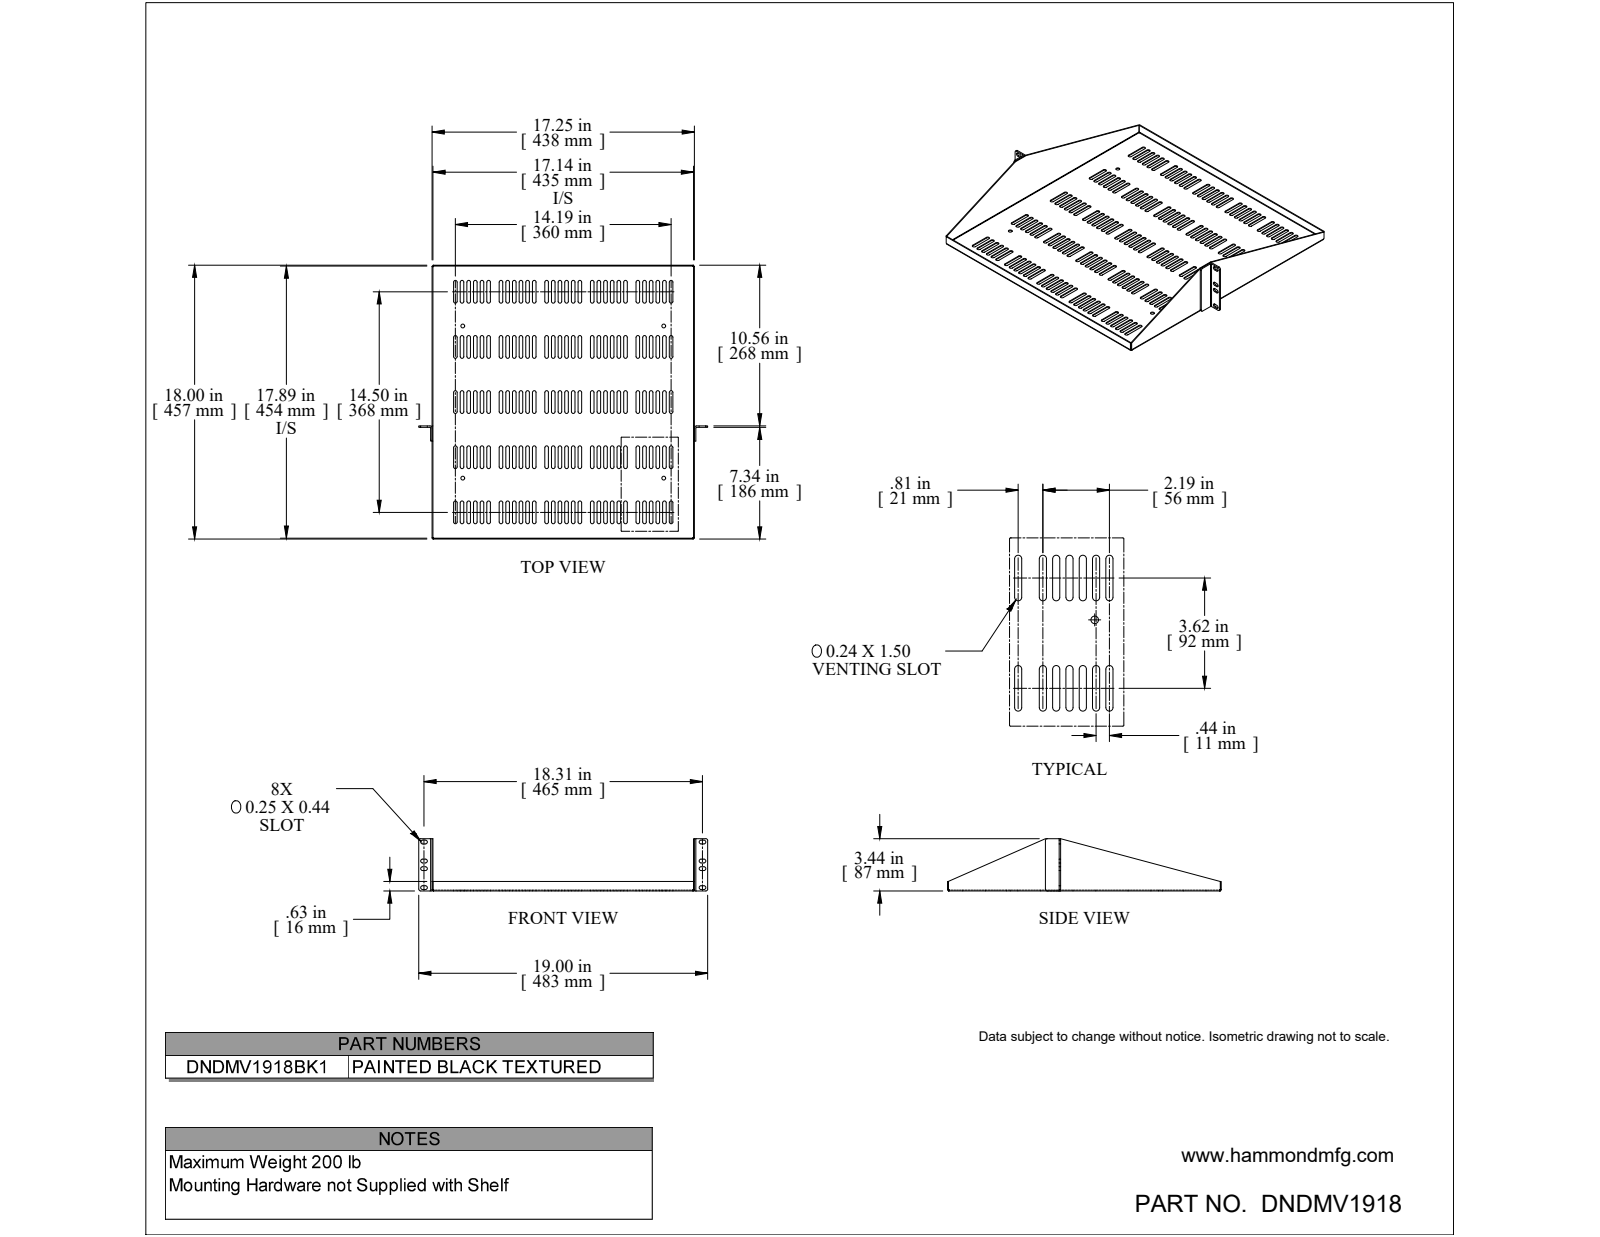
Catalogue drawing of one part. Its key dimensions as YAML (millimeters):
part_name: "DNDMV1918BK1"
step_written_by: "SolidWorks 2019 (CONFIG_CONTROL_DESIGN)"
units: millimeters
bodies: {solids: 3, faces: 714, planar: 358, cylindrical: 348, other: 8}
overall_size: [482.6, 457.2, 87.3]
volume: 344600
surface_area: 489200
round_holes:
  - {diameter: 6.4, count: 4}
partial_cylinders:
  - {radius: 3, count: 270}
  - {radius: 3, count: 30}
  - {radius: 3.2, count: 22}
  - {radius: 0.7, count: 4}
  - {radius: 1.4, count: 4}
  - {radius: 2.2, count: 4}
  - {radius: 1.2, count: 2}
  - {radius: 3.6, count: 2}
face_to_face_distances: [1.4, 1.4, 436.7, 438.2, 435.3, 455.8, 454.3, 457.2, 2.4, 3.9]
hole_center_spacings: [254, 335.7, 421]
